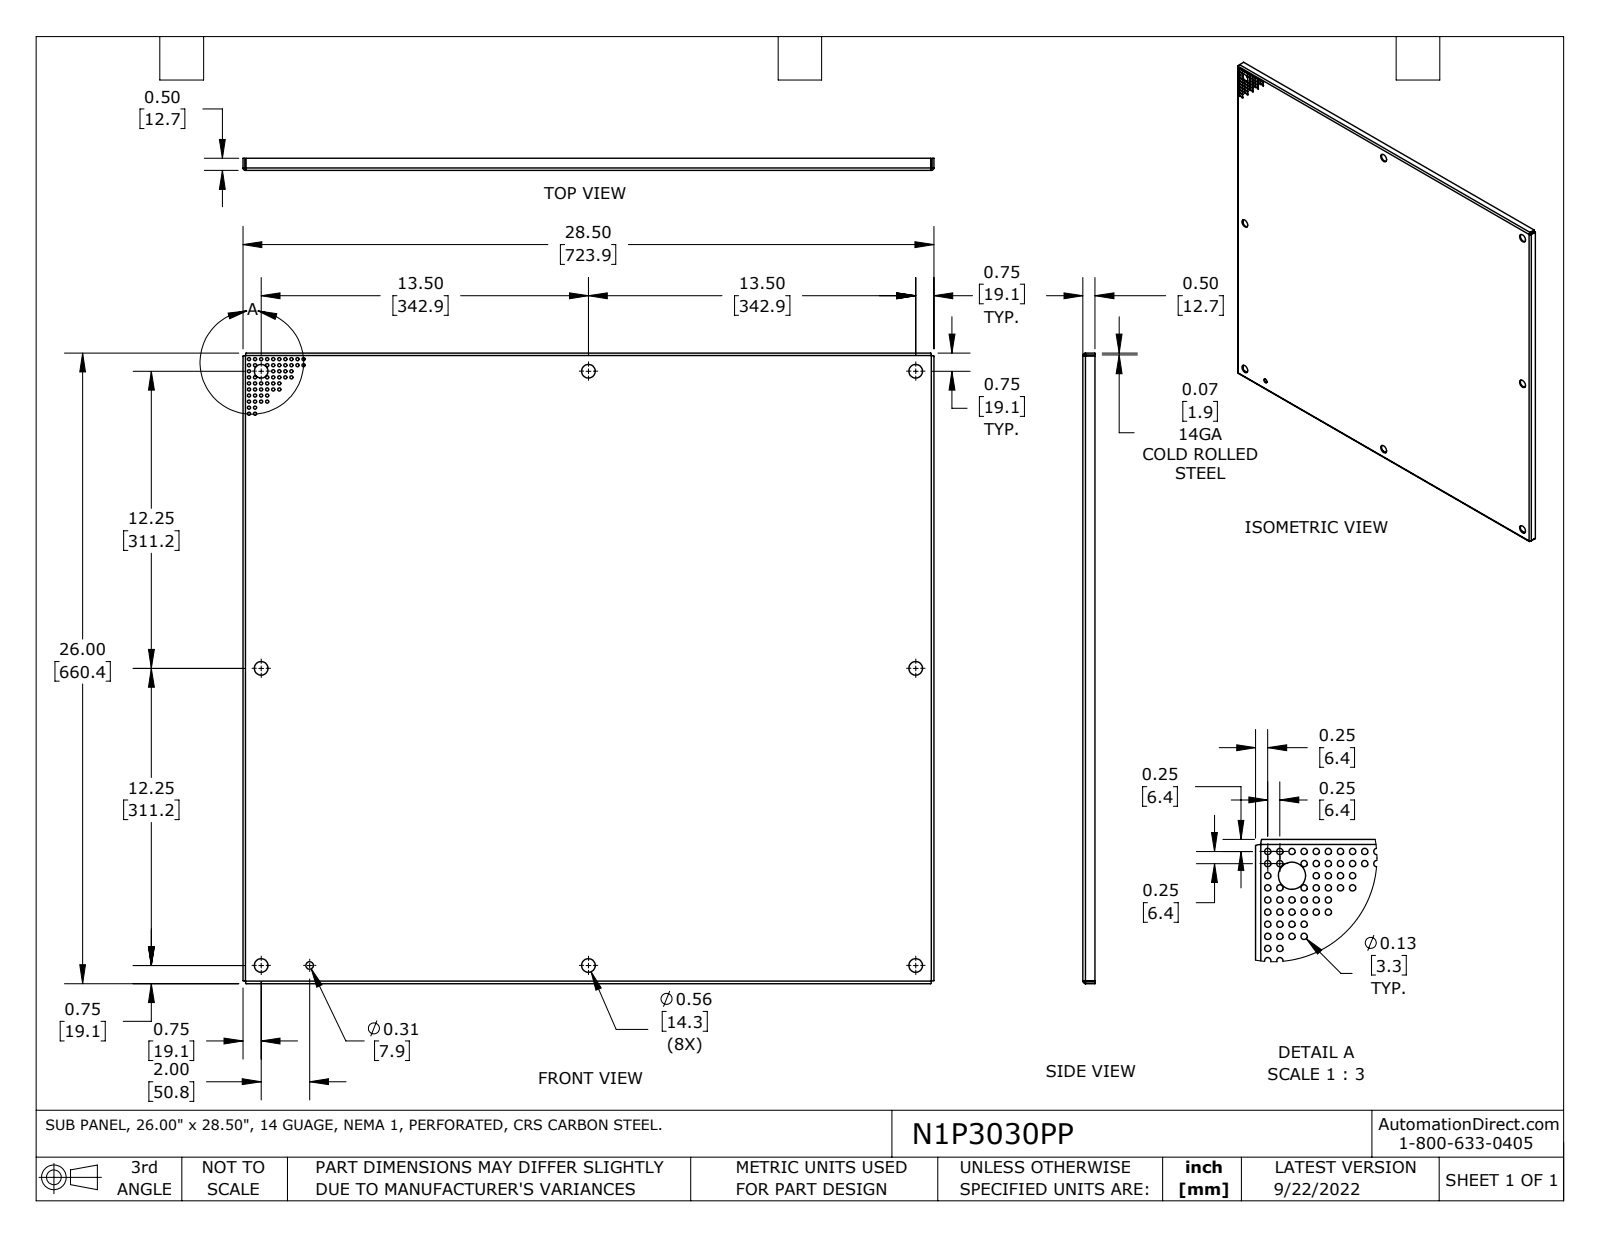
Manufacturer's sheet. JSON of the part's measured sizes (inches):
{"part_name": "N1P3030PP", "step_written_by": "SolidWorks 2021 (AUTOMOTIVE_DESIGN)", "units": "inches", "bodies": {"solids": 1, "faces": 166, "planar": 22, "cylindrical": 136, "other": 8}, "overall_size": [28.5, 26, 0.5], "volume_in3": 57.79, "surface_area_in2": 1573, "round_holes": [[0.13, 55], [0.563, 8], [0.312, 1]], "partial_cylinders_radius": [[0.031, 4], [0.105, 4]], "face_to_face_distances": [0.074, 25.926, 28.426, 26, 25.852, 28.5, 28.352, 0.426, 0.5, 0.126], "hole_center_spacings": [0.25, 0.559, 1.25, 0.791, 0.5, 1.031, 0.354, 0.902]}
